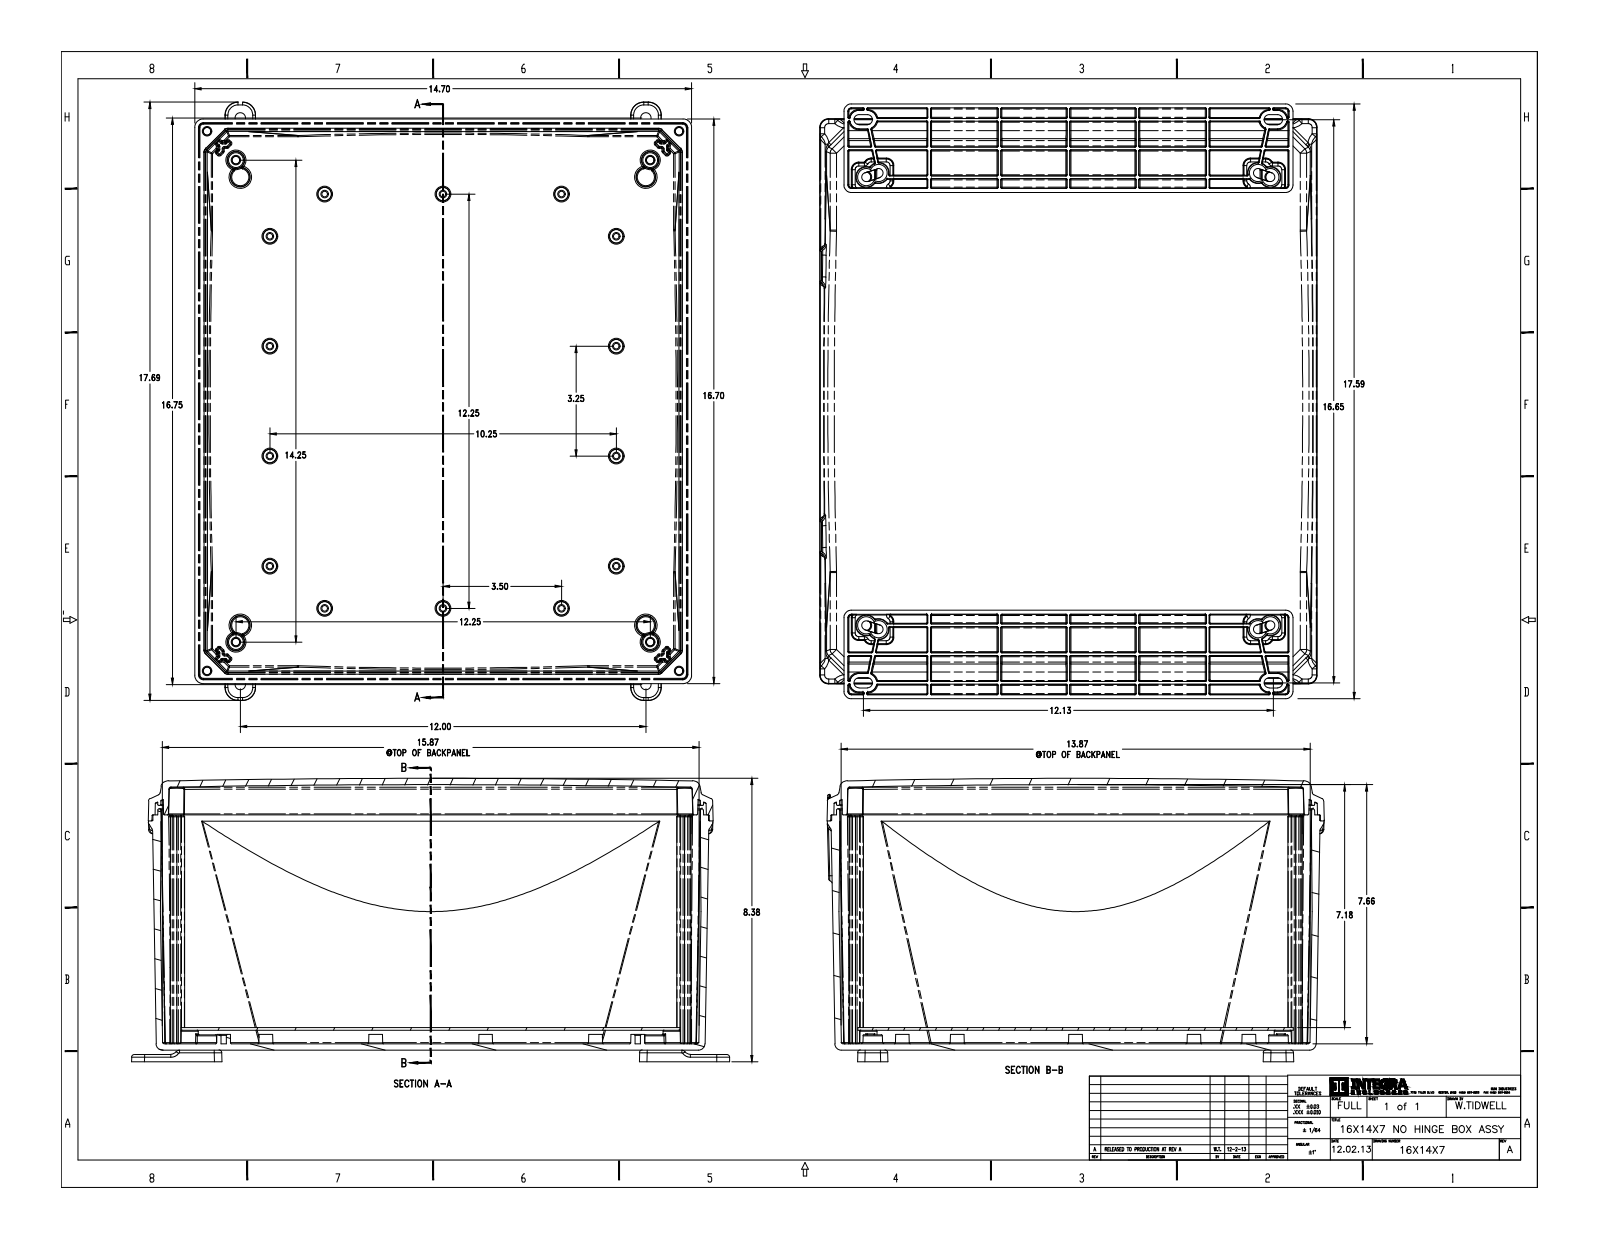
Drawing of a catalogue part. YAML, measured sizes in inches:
part_name: "H161407SF-P10"
step_written_by: "SolidWorks 2018 (AUTOMOTIVE_DESIGN)"
units: inches
bodies: {solids: 26, faces: 3402, planar: 703, cylindrical: 1175, other: 1524}
overall_size: [17.69, 14.705, 8.38]
volume: 190.1
surface_area: 2042
round_holes:
  - {diameter: 0.16, count: 14}
  - {diameter: 0.19, count: 8}
  - {diameter: 0.15, count: 4}
  - {diameter: 0.201, count: 4}
  - {diameter: 0.242, count: 4}
round_bosses_or_shafts:
  - {diameter: 0.3, count: 8}
  - {diameter: 0.298, count: 8}
  - {diameter: 0.29, count: 8}
  - {diameter: 0.26, count: 8}
  - {diameter: 0.258, count: 8}
  - {diameter: 0.25, count: 8}
  - {diameter: 0.375, count: 4}
  - {diameter: 0.372, count: 4}
partial_cylinders:
  - {radius: 0.03, count: 227}
  - {radius: 0.02, count: 130}
  - {radius: 0.005, count: 80}
  - {radius: 0.08, count: 45}
  - {radius: 0.04, count: 29}
  - {radius: 0.09, count: 26}
  - {radius: 0.01, count: 24}
  - {radius: 0.13, count: 20}
face_to_face_distances: [0.188, 0.588, 0.392, 0.196, 6.96, 6.772, 0.188, 0.18, 6.78, 6.592]
hole_center_spacings: [12.135, 10.752, 12.25, 0.515, 1.207, 1.67, 1.957, 2.05]
